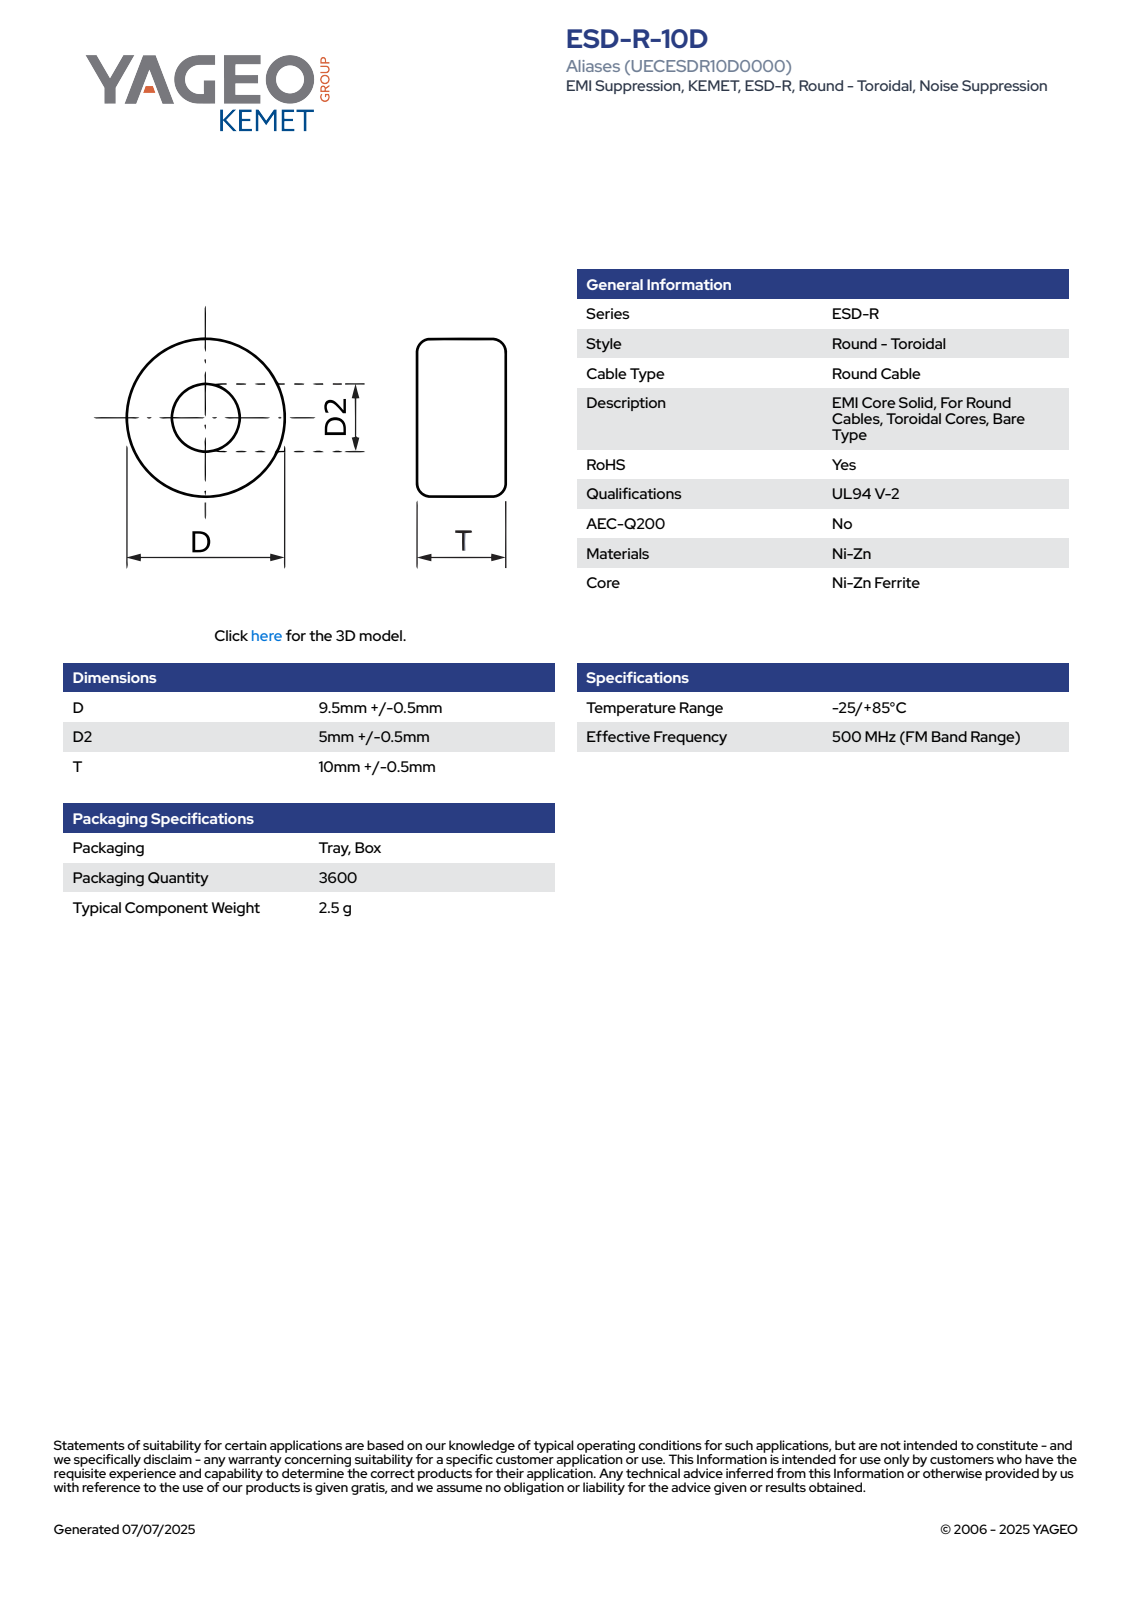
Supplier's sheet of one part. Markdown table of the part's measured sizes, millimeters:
| quantity | value |
| --- | --- |
| part name | EC_KBC_D10D25T10.5 |
| STEP written by | SolidWorks 2021 (AUTOMOTIVE_DESIGN) |
| units | millimeters |
| bodies | 1 solid, 66 faces (24 planar, 7 cylindrical, 35 other) |
| overall size | 10.5 × 10.01 × 10 |
| volume | 617 mm³ |
| surface area | 605 mm² |
| round holes (diameter × count) | 5 × 1 |
| round bosses / shafts (diameter × count) | 10 × 1 |
| partial cylindrical surfaces (radius × count) | 5.01 × 1 |
| main face-to-face distances | 10.5, 4.4, 6.1, 1.7, 0.32, 4.72, 5.78, 1.38, 1.06, 5.46 |
